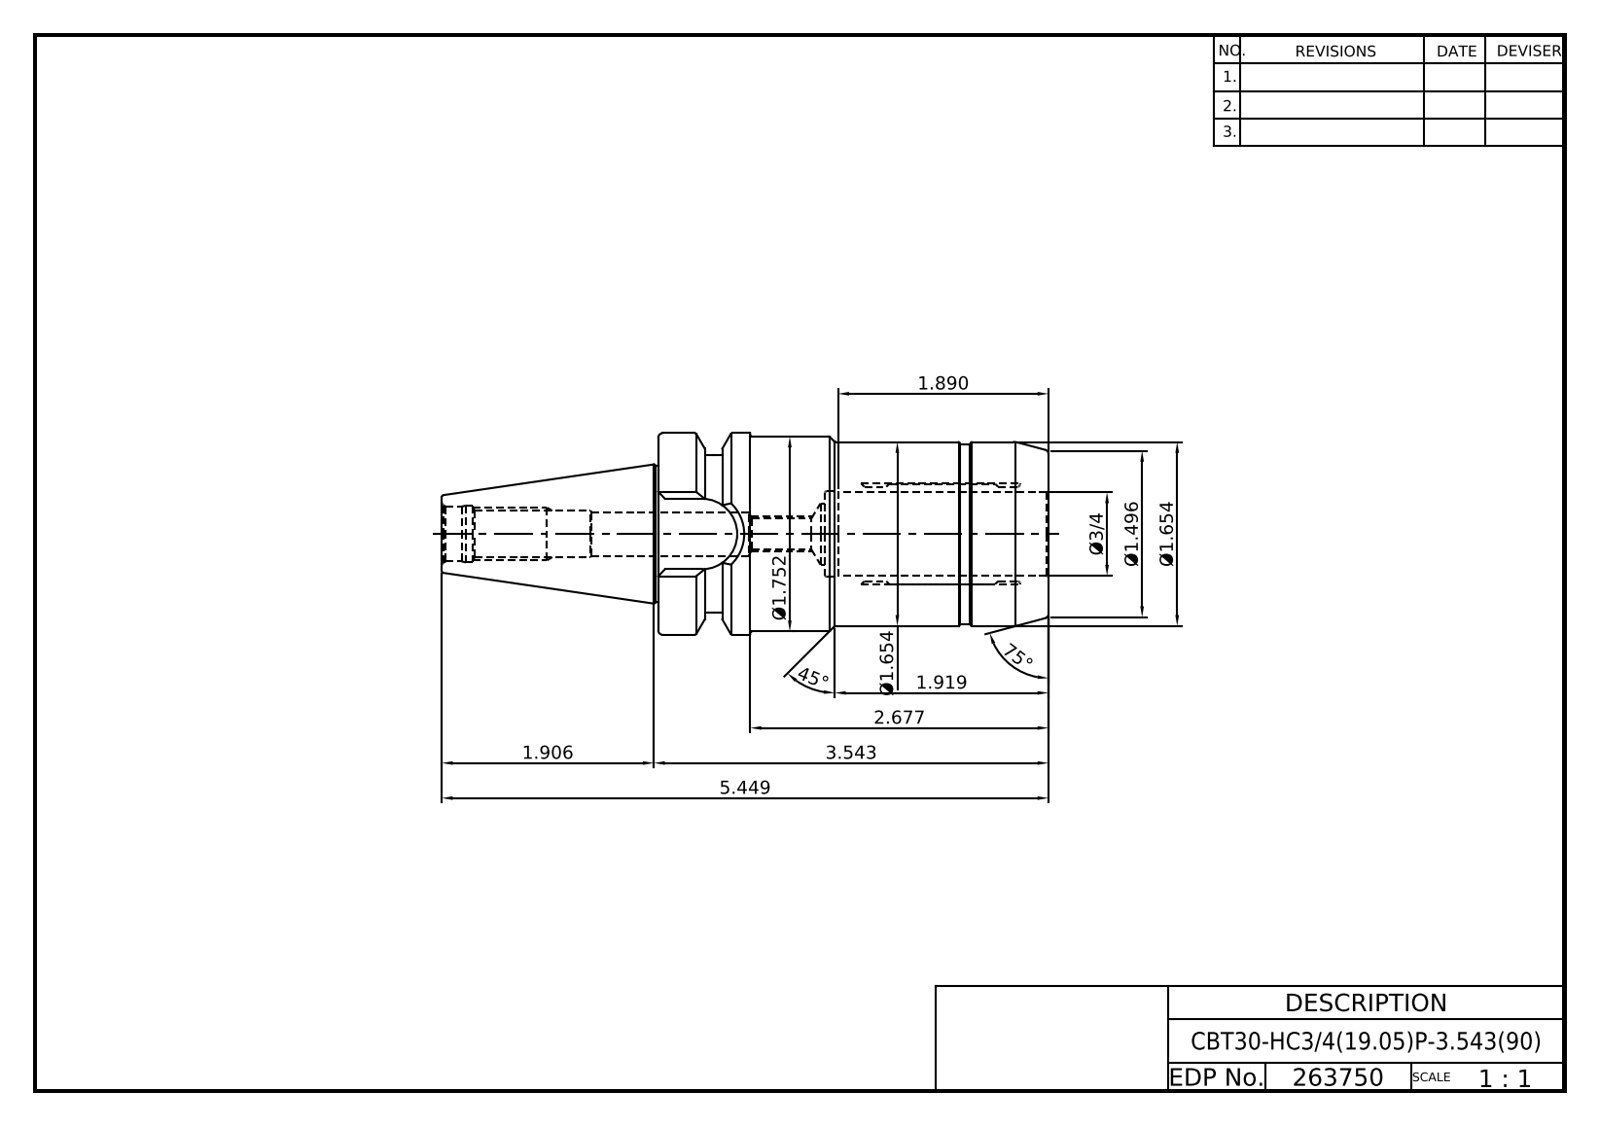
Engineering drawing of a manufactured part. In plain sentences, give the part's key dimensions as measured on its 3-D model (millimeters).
The part is named "CBT30-HC19.05P-90". Its 3-D file was written by "Autodesk Inventor 2020 (AUTOMOTIVE_DESIGN)". It is 1 solid with 76 faces: 22 planar, 24 cylindrical and 30 other. Overall it measures 138.4 by 46 by 46 millimeters. Its volume is 128 200 cubic millimeters and its surface area 24 673 square millimeters. Round holes: 1 of diameter 6.92, 1 of diameter 10, 1 of diameter 10.11, 1 of diameter 12.5, 1 of diameter 13.1, 1 of diameter 14, 1 of diameter 19.05, 1 of diameter 19.55. Round bosses or shafts: 1 of diameter 46, 1 of diameter 44.5, 1 of diameter 42, 1 of diameter 41, 1 of diameter 31.2. Partial cylindrical surfaces (rounded edges, fillets, slot ends): 1 of radius 8.05, 1 of radius 18. The main face-to-face distances are 89, 32.6, 14.6, 74.4, 10.6, 4, 78.4, 38, 27.4, 23.4.
